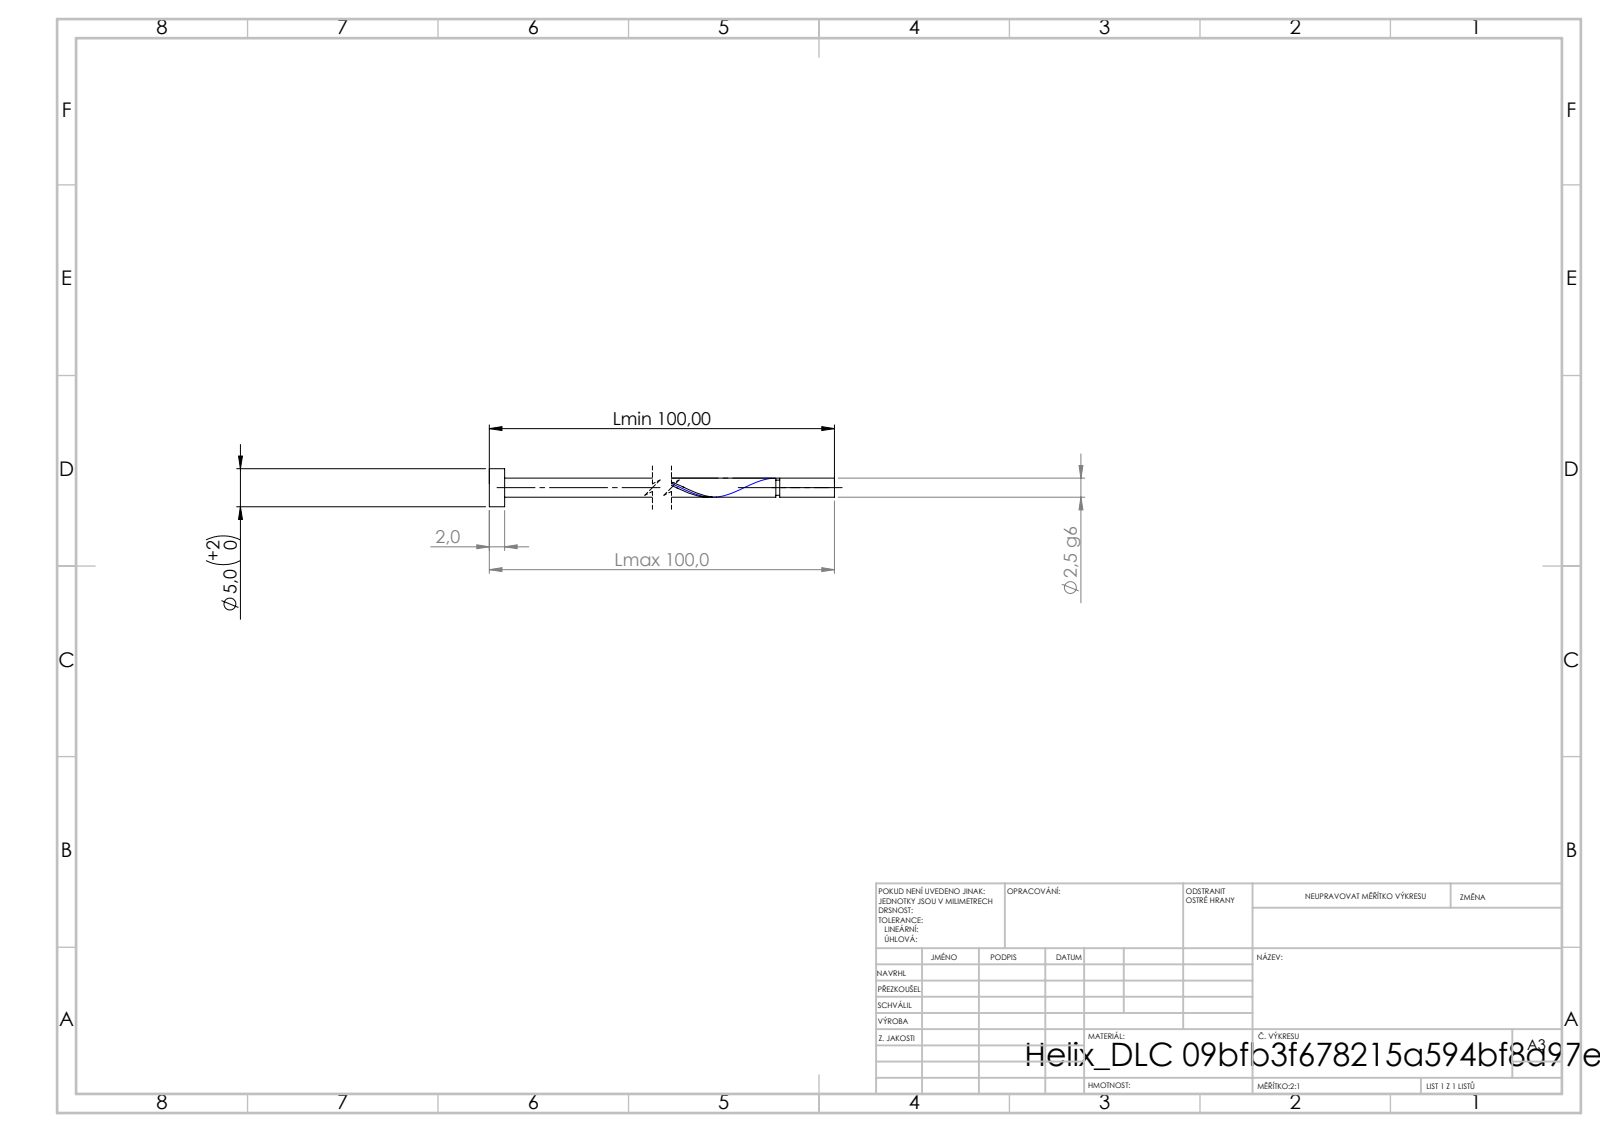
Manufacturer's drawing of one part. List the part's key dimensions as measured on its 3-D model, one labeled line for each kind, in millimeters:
STEP written by: SolidWorks 2019 (CONFIG_CONTROL_DESIGN)
Units: millimetres
Bodies: 1 solid, 21 faces (6 planar, 14 cylindrical, 1 other)
Overall size (bounding box): 100 × 5 × 5
Volume: 515 mm³ · Surface area: 857 mm²
Round bosses / shafts (diameter × count): ⌀5 ×1, ⌀2.5 ×1, ⌀2 ×1
Main face-to-face distances: 2, 100, 98, 92.81, 90.81, 7.19, 92.31, 90.31, 0.5, 7.69
